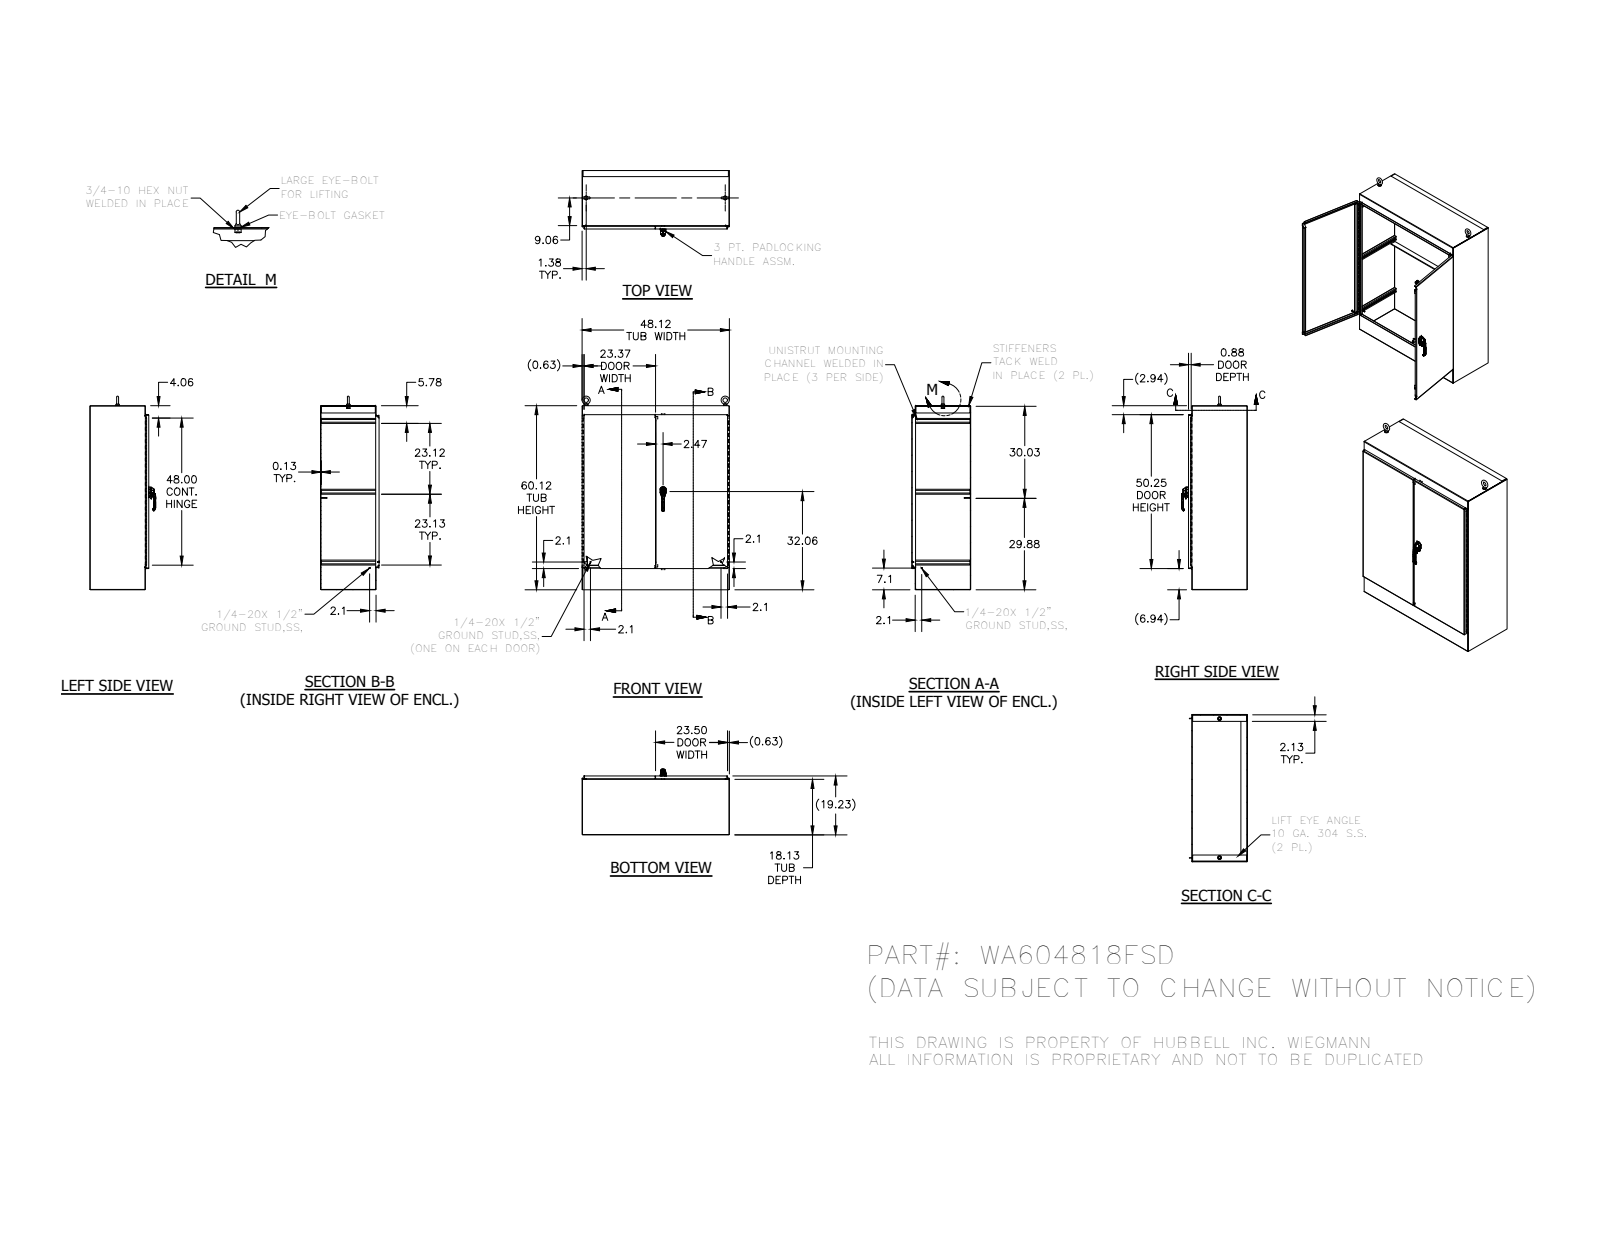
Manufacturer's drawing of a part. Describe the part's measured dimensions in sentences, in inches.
The part is named "FUN00101; HFW3025; 316298; 349132 (+8 more)". Its 3-D file was written by "Autodesk Inventor 2014 (AUTOMOTIVE_DESIGN)". It is 66 solids with 3352 faces: 1497 planar, 1117 cylindrical and 738 other. Overall it measures 63.248 by 48.13 by 21.498 inches. Its volume is 1 470 cubic inches and its surface area 23 510 square inches. Round holes: 16 of diameter 0.375, 8 of diameter 0.276, 4 of diameter 0.2, 3 of diameter 0.213, 3 of diameter 0.236, 3 of diameter 0.28, 2 of diameter 0.142, 2 of diameter 0.18, 2 of diameter 0.241, 2 of diameter 0.25, 2 of diameter 0.252, 2 of diameter 0.4. Round bosses or shafts: 3 of diameter 0.337, 3 of diameter 0.25, 2 of diameter 1.25, 2 of diameter 1.12, 2 of diameter 1, 2 of diameter 0.75, 2 of diameter 0.563, 2 of diameter 0.526. Partial cylindrical surfaces (rounded edges, fillets, slot ends): 166 of radius 0.02, 89 of radius 0.012, 24 of radius 0.031, 20 of radius 0.125, 19 of radius 0.019, 17 of radius 0.156, 16 of radius 0.01, 15 of radius 0.079. The main face-to-face distances are 0.125, 0.125, 19.105, 18.98, 19.23, 19.104, 48, 60, 18, 47.875. The hole center spacings are 5.333, 16, 10.667, 46.783, 46.935, 47.237, 21.333, 48.28.
